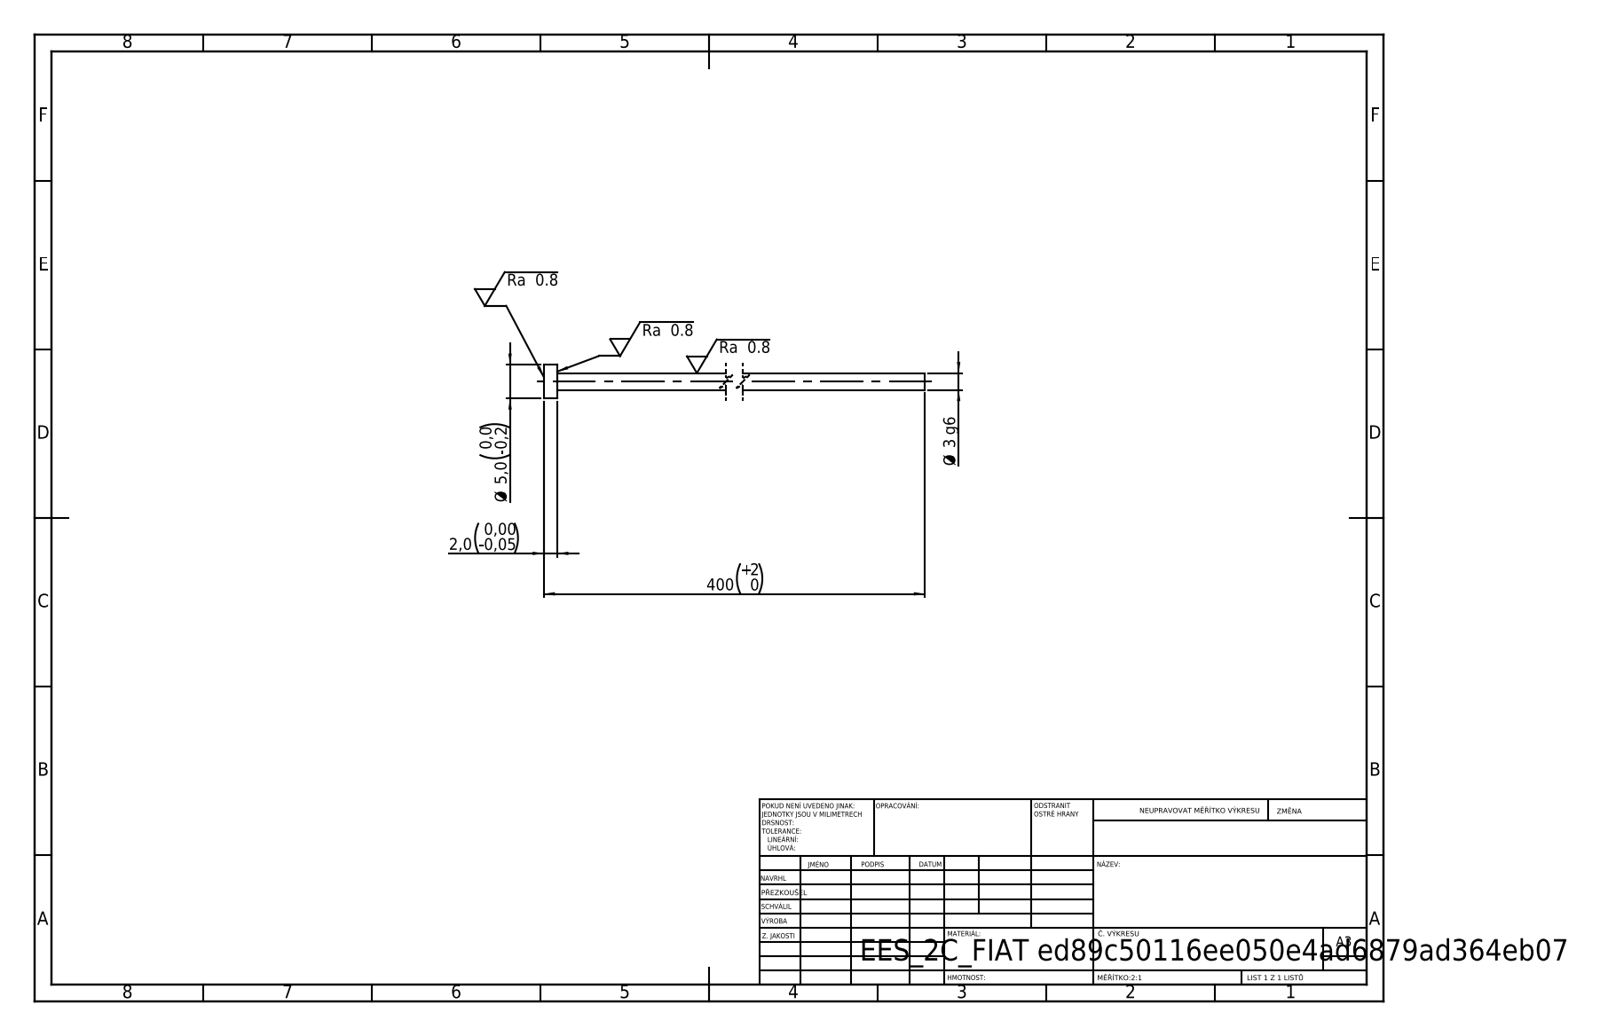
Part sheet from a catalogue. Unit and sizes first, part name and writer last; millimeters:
Units: millimetres
Overall size (bounding box): 400 × 5 × 5
Round bosses / shafts (diameter × count): ⌀5 ×1, ⌀2.5 ×1
Main face-to-face distances: 2, 400, 398
Volume: 1 993 mm³ · Surface area: 3 197 mm²
Bodies: 1 solid, 7 faces (3 planar, 4 cylindrical, 0 other)
STEP written by: SolidWorks 2019 (CONFIG_CONTROL_DESIGN)
